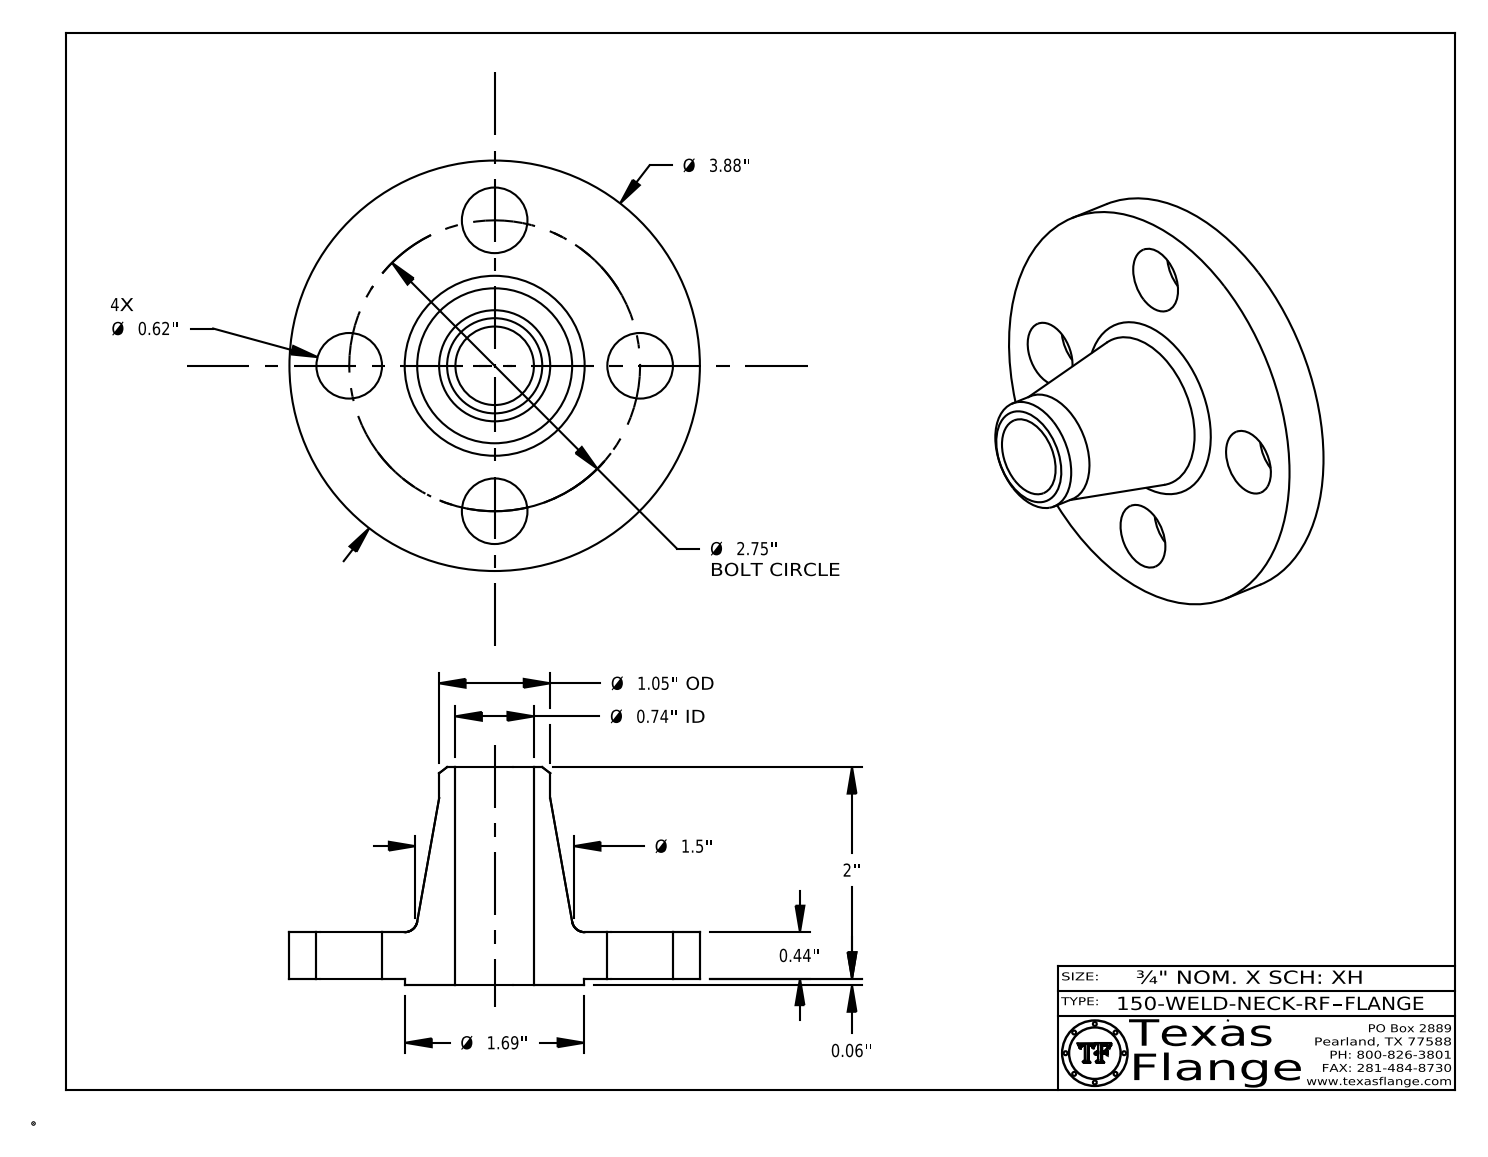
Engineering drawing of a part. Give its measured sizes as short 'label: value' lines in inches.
name: 150-WELD-NECK-RF
written by: CATIA V5 STEP AP214 (AUTOMOTIVE_DESIGN)
unit: in
bodies: 1 solid, 411 faces (369 planar, 36 cylindrical, 6 other)
size: 3.88 × 3.88 × 2.063
volume: 5.809 in³; area: 39.33 in²
holes: 4× ⌀0.62, 1× ⌀0.495, 1× ⌀0.742
bosses: 8× ⌀0.03, 1× ⌀3.88, 1× ⌀1.69, 1× ⌀1.05, 1× ⌀0.39
face distances: 0.44, 0.063, 0.503, 2.063, 2, 1.56, 0.488, 0.425, 0.015, 1.575
hole spacings: 1.375, 1.945, 1.052, 2.541, 2.75
